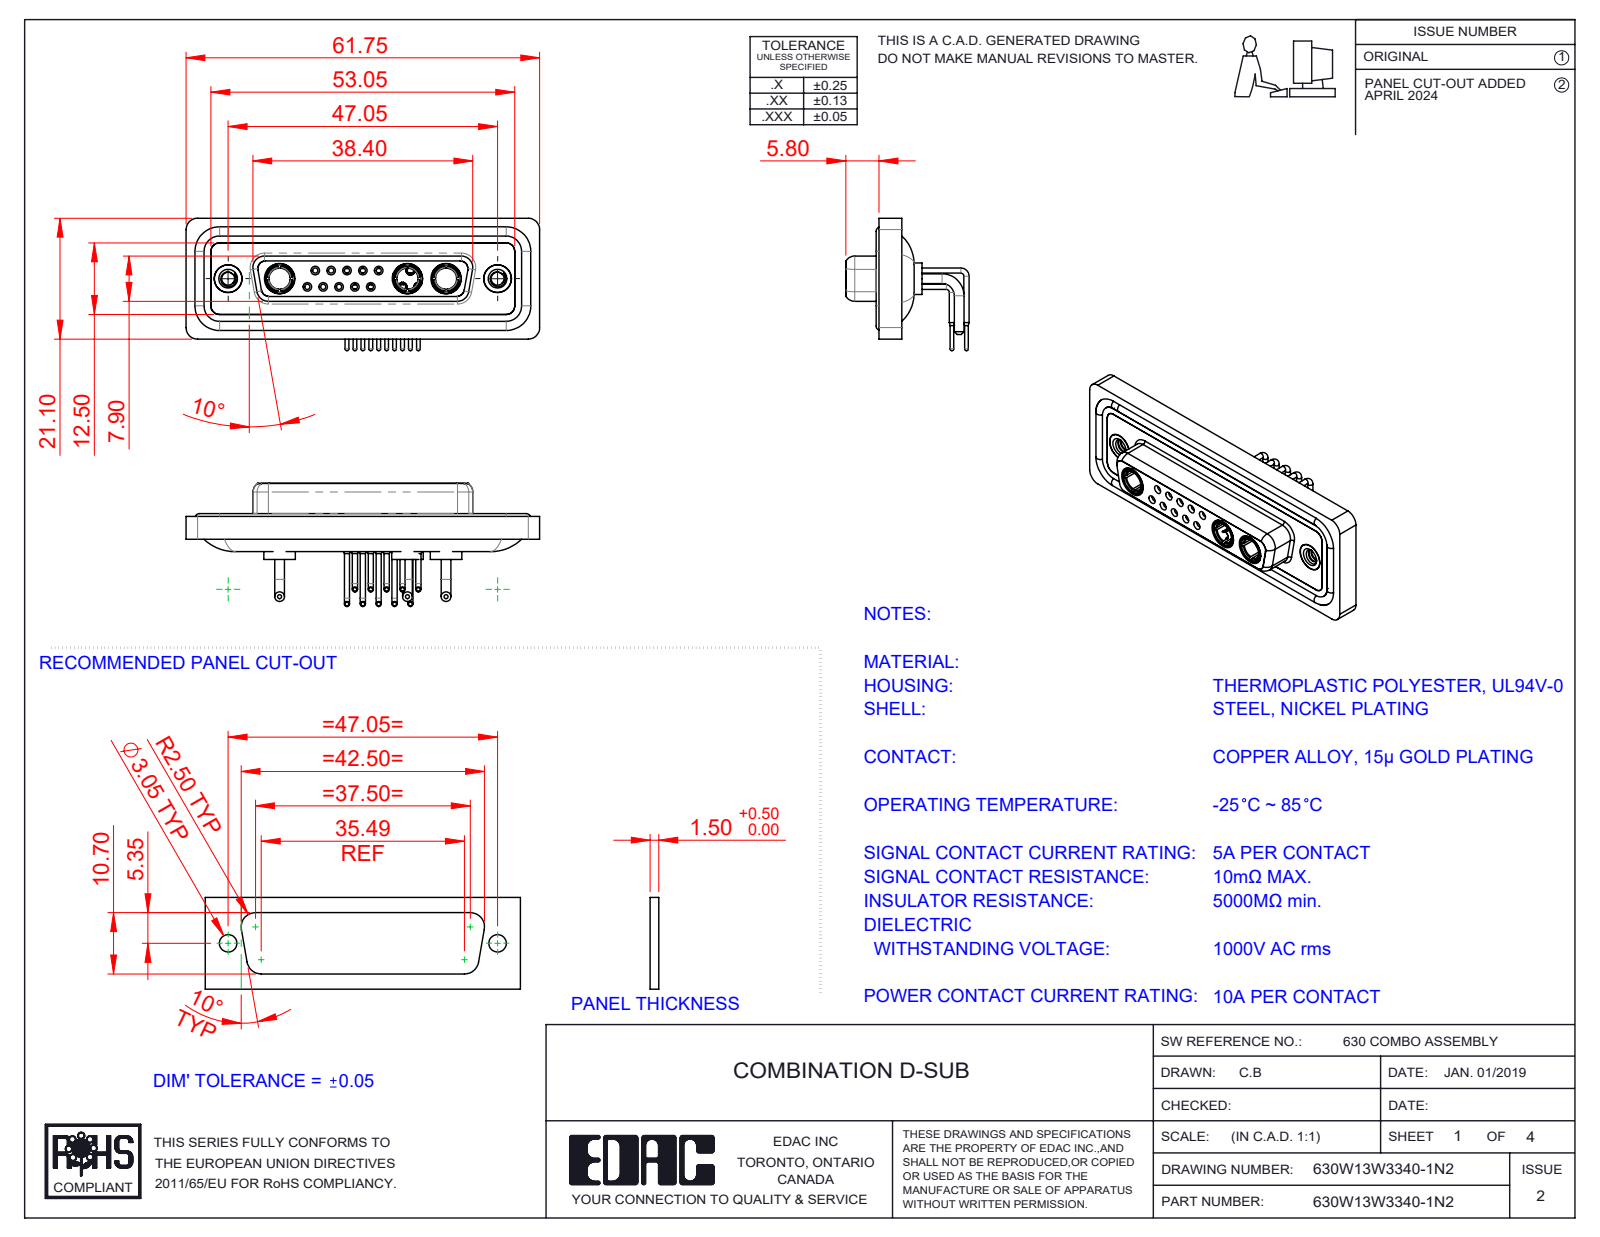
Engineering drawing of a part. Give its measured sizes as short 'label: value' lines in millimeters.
name: Power Socket_10A RA; 630Combo Waterproof Housing_25 Contacts; 630Combo Threaded Rivet_2; 630W13W3340-1N2 (+5 more)
written by: SolidWorks 2023 (CONFIG_CONTROL_DESIGN)
unit: mm
bodies: 23 solids, 1150 faces (342 planar, 493 cylindrical, 315 other)
size: 61.75 × 23.12 × 21.53
volume: 8 297 mm³; area: 14 144 mm²
holes: 10× ⌀0.9, 10× ⌀1.1, 10× ⌀1.5, 10× ⌀2, 5× ⌀1.6, 5× ⌀1.7, 5× ⌀4.85, 3× ⌀3.7, 3× ⌀5.3, 2× ⌀2.26, 2× ⌀4, 2× ⌀4.05
bosses: 15× ⌀0.9, 12× ⌀1.6, 10× ⌀0.65, 6× ⌀1.7, 5× ⌀2, 5× ⌀1.5, 3× ⌀5.5, 3× ⌀5.2
rounds: 18× R1.5, 18× R2, 8× R1.35, 8× R1.6, 4× R0.25, 4× R0.5, 4× R0.6, 4× R0.65
face distances: 0.4, 1.8, 4.1, 1.1, 1.6, 1.5, 3.1, 2.5, 3.7, 1.4
hole spacings: 3.16, 2.77, 5.54, 5.04, 8.31, 5.03, 7.49, 11.08
